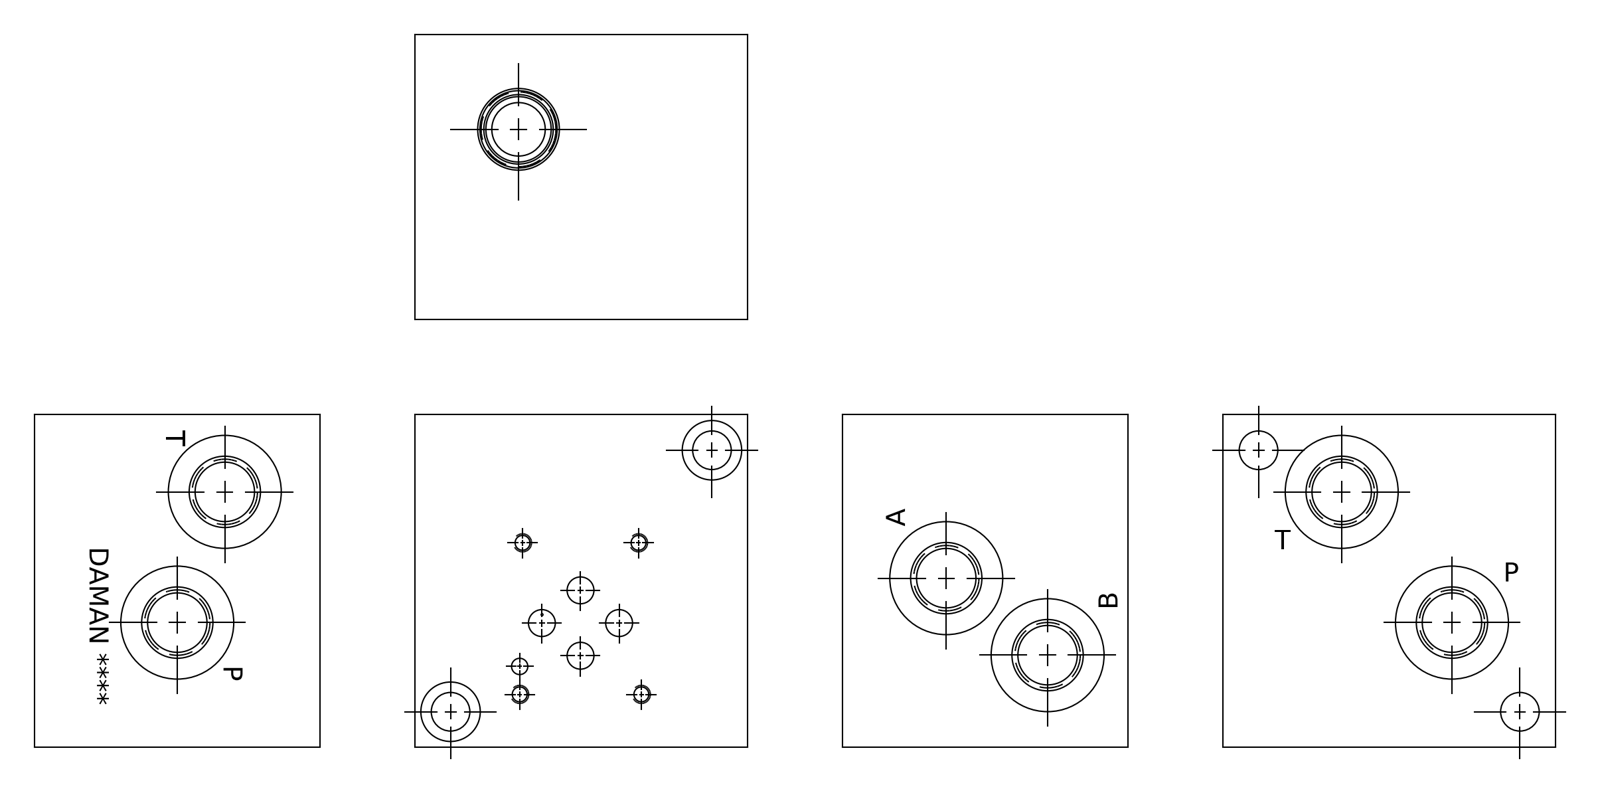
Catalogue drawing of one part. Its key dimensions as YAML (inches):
part_name: "Part__D03SPRVS8S_3D"
step_written_by: "Autodesk Inventor 2020 (AUTOMOTIVE_DESIGN)"
units: inches
bodies: {solids: 1, faces: 563, planar: 315, cylindrical: 53, other: 195}
overall_size: [3.5, 3.5, 3]
volume: 32.22
surface_area: 93.84
round_holes:
  - {diameter: 0.625, count: 8}
  - {diameter: 0.689, count: 6}
  - {diameter: 0.75, count: 6}
  - {diameter: 0.758, count: 6}
  - {diameter: 1.206, count: 6}
  - {diameter: 0.149, count: 4}
  - {diameter: 0.19, count: 4}
  - {diameter: 0.281, count: 4}
  - {diameter: 0.406, count: 2}
  - {diameter: 0.156, count: 1}
  - {diameter: 0.531, count: 1}
  - {diameter: 0.687, count: 1}
face_to_face_distances: [3.5, 3, 0.031, 3.469, 0.125, 2.875, 3.438, 0.562, 2.438, 2.313]
hole_center_spacings: [0.741, 0.758, 0.868, 1.321, 1.335, 1.594, 2.026, 0.25]
